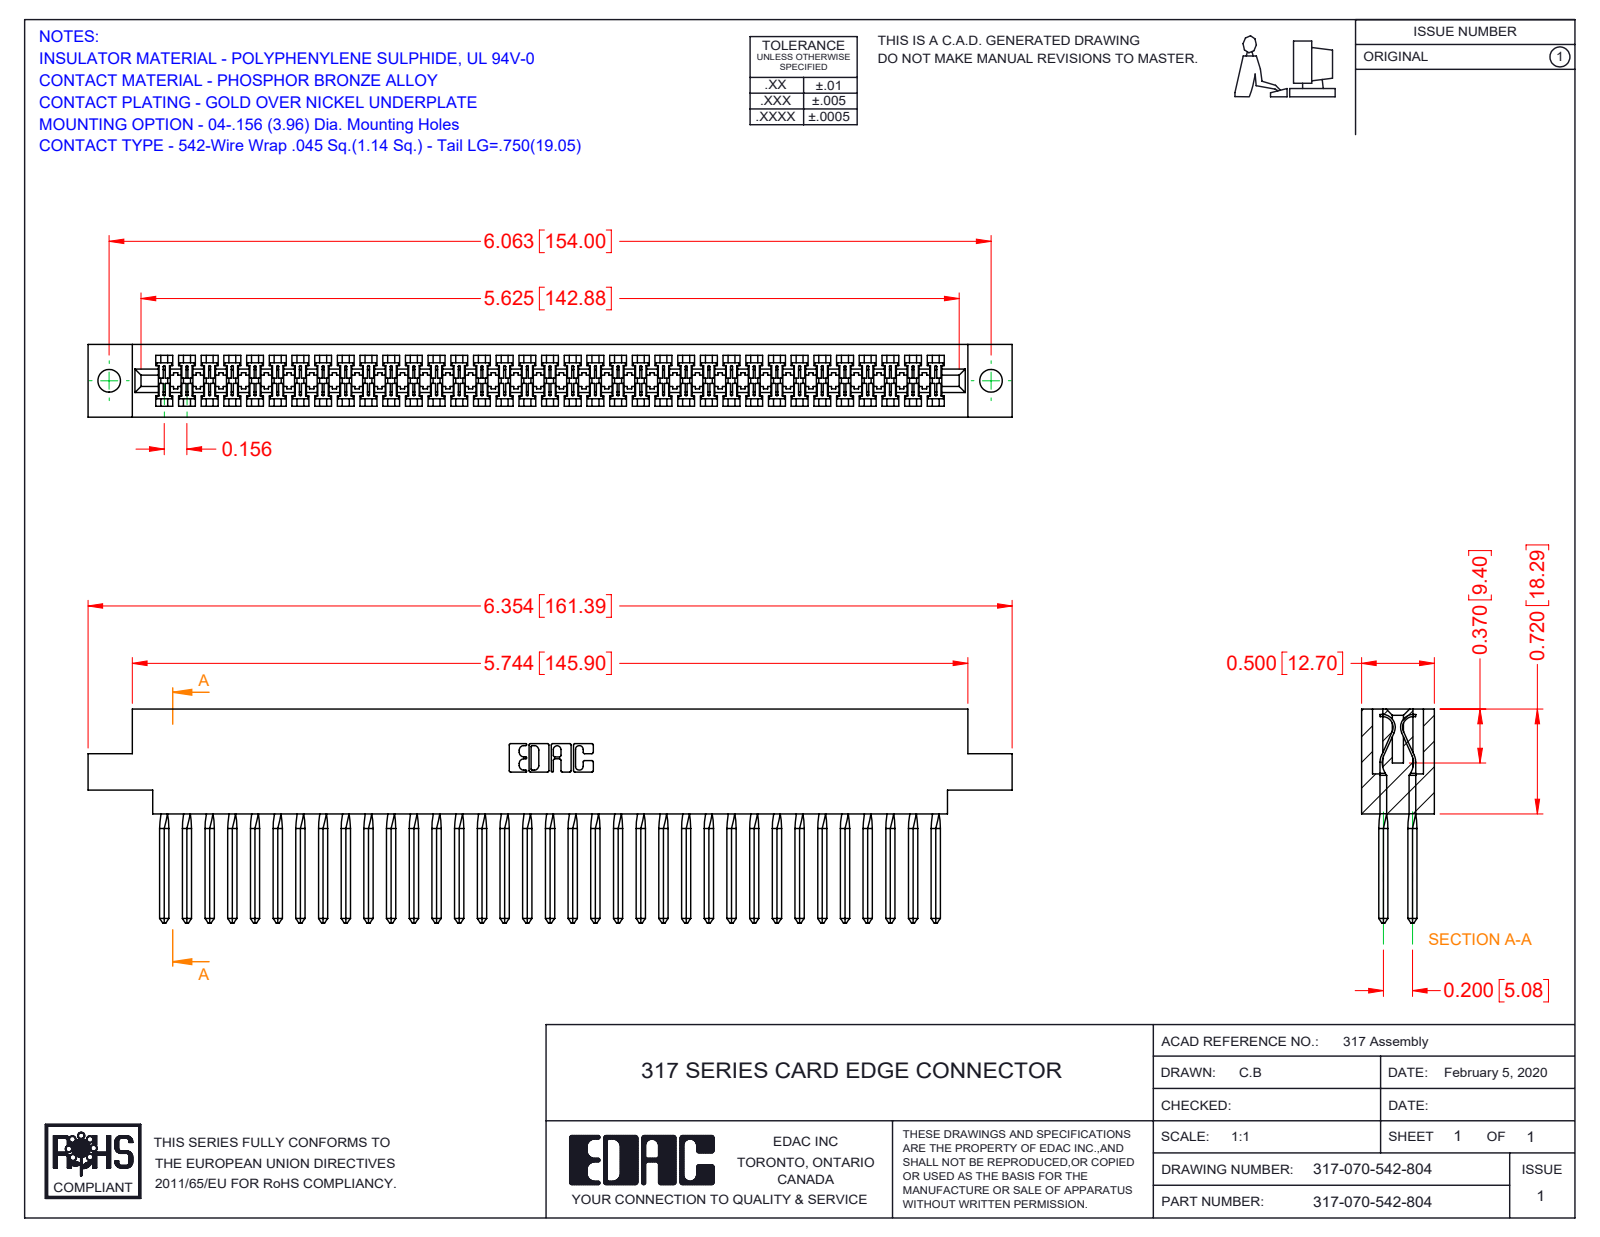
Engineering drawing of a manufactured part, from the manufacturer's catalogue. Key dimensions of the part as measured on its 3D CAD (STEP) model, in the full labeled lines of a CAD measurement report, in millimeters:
Part name (STEP PRODUCT): 317-070-542-804; 317 Part_.156 Dia - TH; 317-290-003_542
STEP written by: SolidWorks 2016 (CONFIG_CONTROL_DESIGN)
Units: millimetres
Bodies: 71 solids, 4092 faces (3278 planar, 534 cylindrical, 280 other)
Overall size (bounding box): 161.4 × 37.3 × 12.7
Volume: 26 120 mm³ · Surface area: 35 910 mm²
Round holes (diameter × count): ⌀4 ×2
Partial cylindrical surfaces — rounded edges, fillets, slot ends (radius × count): R0.2 ×140, R0.3 ×22, R0.2 ×6, R0.8 ×6, R0.7 ×3, R1.9 ×2, R2.3 ×2, R2.5 ×2
Main face-to-face distances: 12.7, 1.9, 10.8, 8.9, 5.1, 1.2, 3.3, 9.4, 1.3, 7.5
Hole centre spacings: 154
